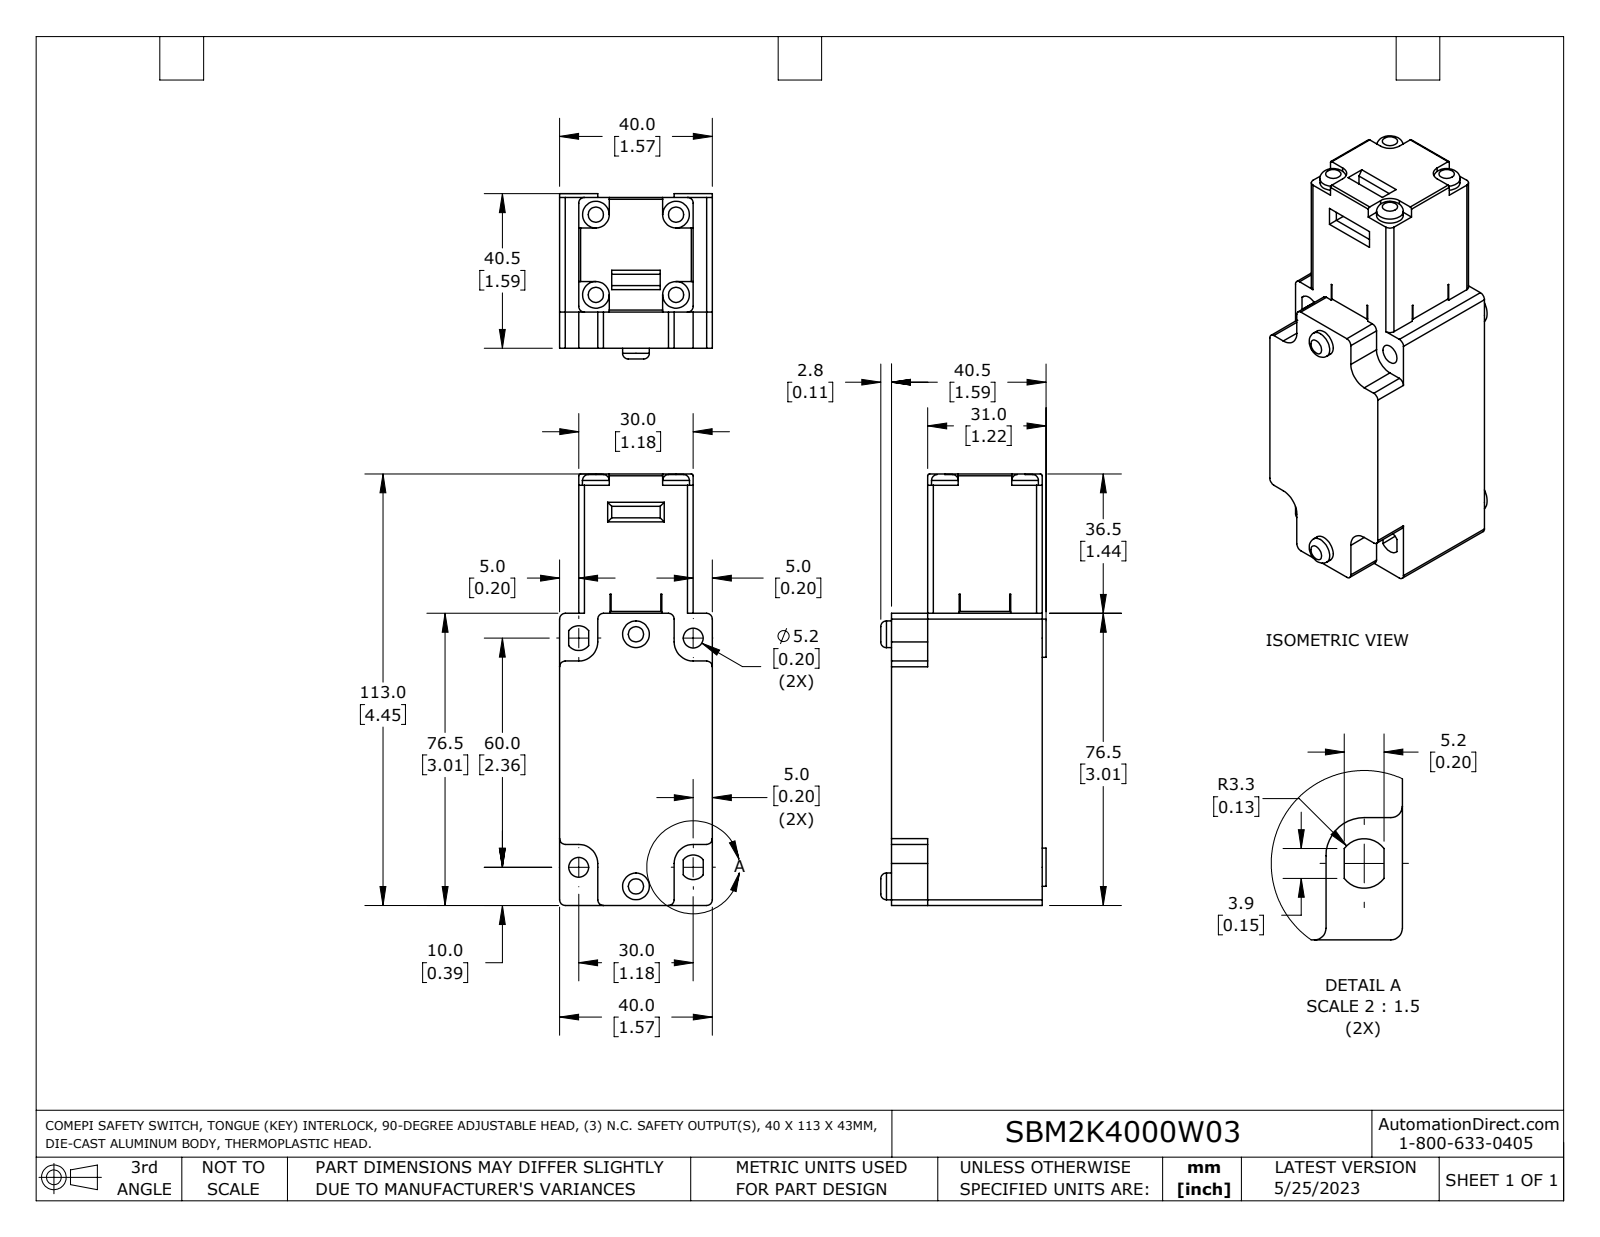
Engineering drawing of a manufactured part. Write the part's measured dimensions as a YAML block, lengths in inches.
part_name: "SBM2K4000W03"
step_written_by: "SolidWorks 2021 (AUTOMOTIVE_DESIGN)"
units: inches
bodies: {solids: 1, faces: 147, planar: 86, cylindrical: 54, other: 7}
overall_size: [4.449, 1.705, 1.575]
volume: 8.506
surface_area: 40.19
round_holes:
  - {diameter: 0.276, count: 4}
  - {diameter: 0.205, count: 2}
  - {diameter: 0.669, count: 1}
  - {diameter: 0.748, count: 1}
round_bosses_or_shafts:
  - {diameter: 0.394, count: 4}
  - {diameter: 0.276, count: 2}
partial_cylinders:
  - {radius: 0.059, count: 16}
  - {radius: 0.02, count: 4}
  - {radius: 0.197, count: 4}
  - {radius: 0.128, count: 2}
  - {radius: 0.453, count: 1}
  - {radius: 0.472, count: 1}
face_to_face_distances: [1.181, 1.575, 1.555, 0.197, 1.378, 0.374, 3.012, 0.118, 0.02, 0.984]
hole_center_spacings: [0.827, 0.557, 0.613, 1.169, 2.641]
